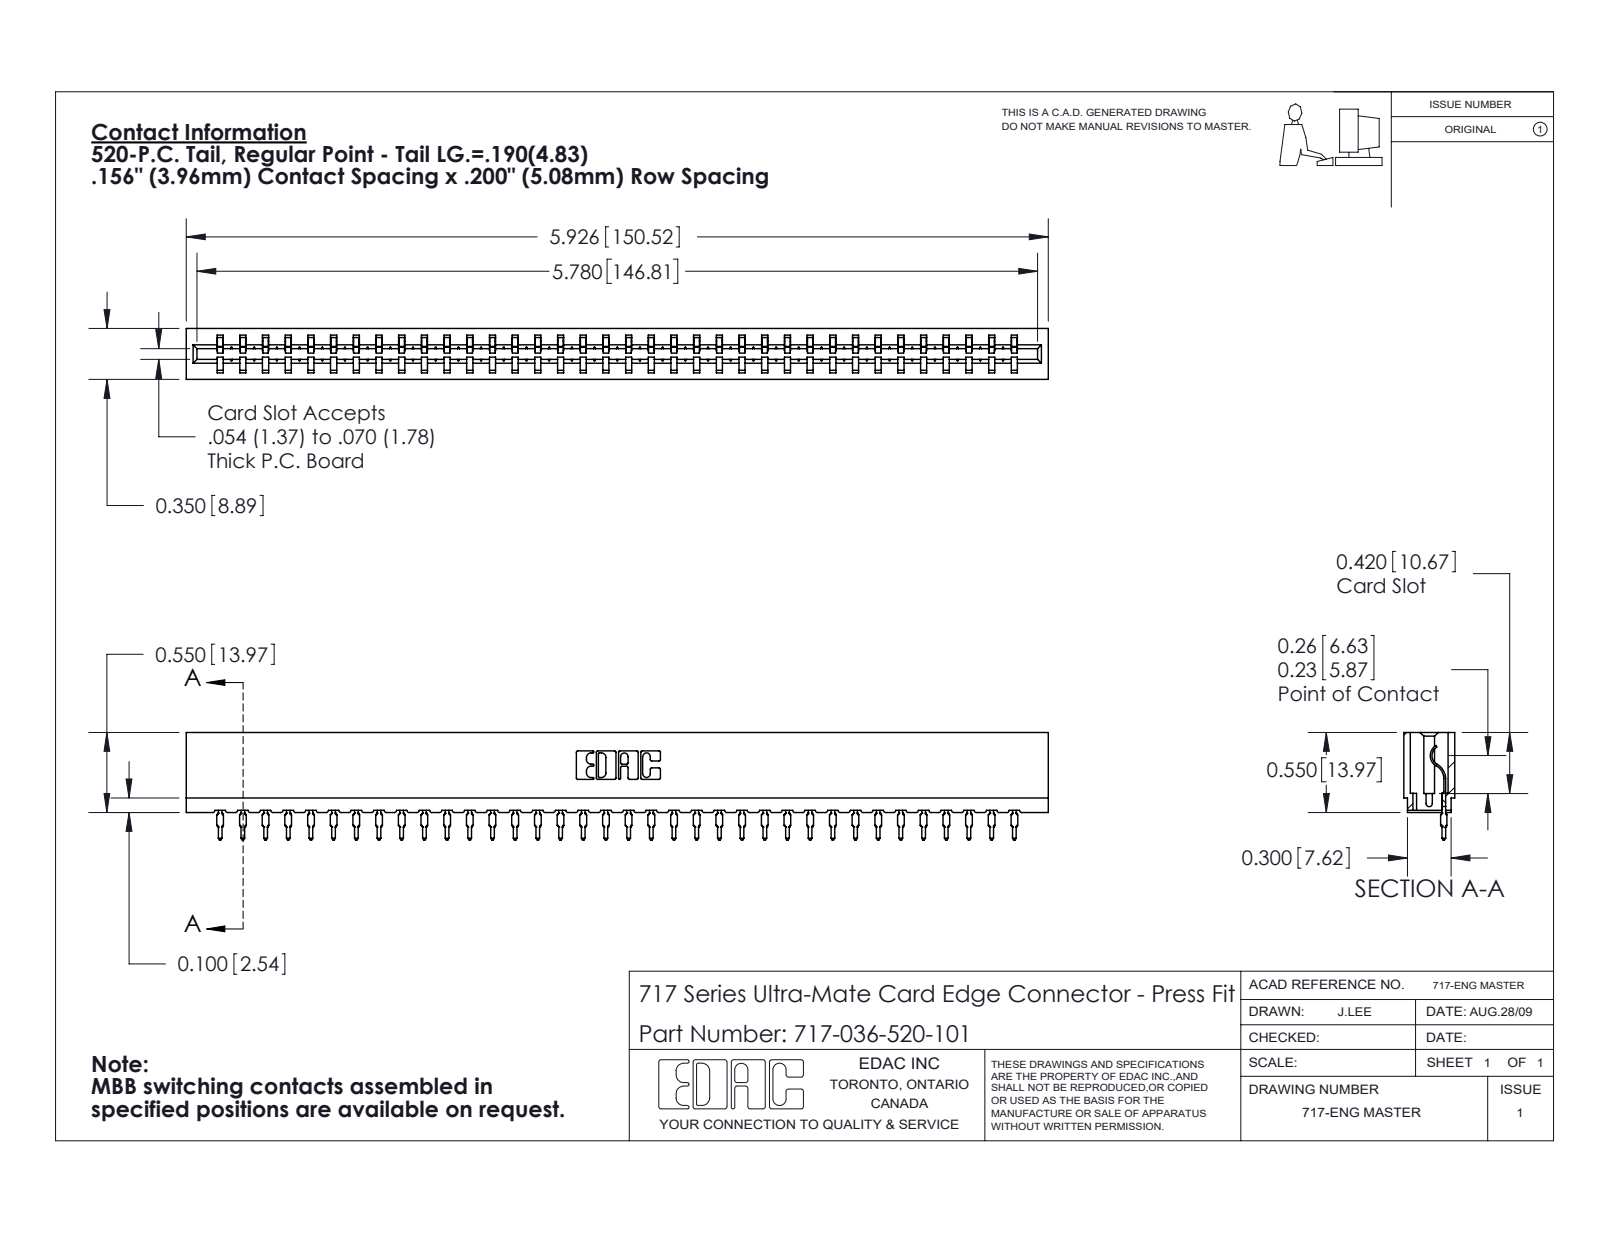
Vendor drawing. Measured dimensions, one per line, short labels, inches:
name: 717 Part_Insulator Option - 06; 745-292-001_520; 717-036-520-101
written by: SolidWorks 2020 (CONFIG_CONTROL_DESIGN)
unit: in
bodies: 37 solids, 4162 faces (2502 planar, 724 cylindrical, 936 other)
size: 5.926 × 0.739 × 0.35
volume: 0.774 in³; area: 27.12 in²
rounds: 72× R0.015, 72× R0.021, 22× R0.01, 6× R0.007, 6× R0.031, 4× R0.005, 4× R0.011, 3× R0.026
face distances: 0.212, 0.138, 0.35, 0.074, 0.045, 0.305, 0.093, 0.167, 0.025, 0.156
